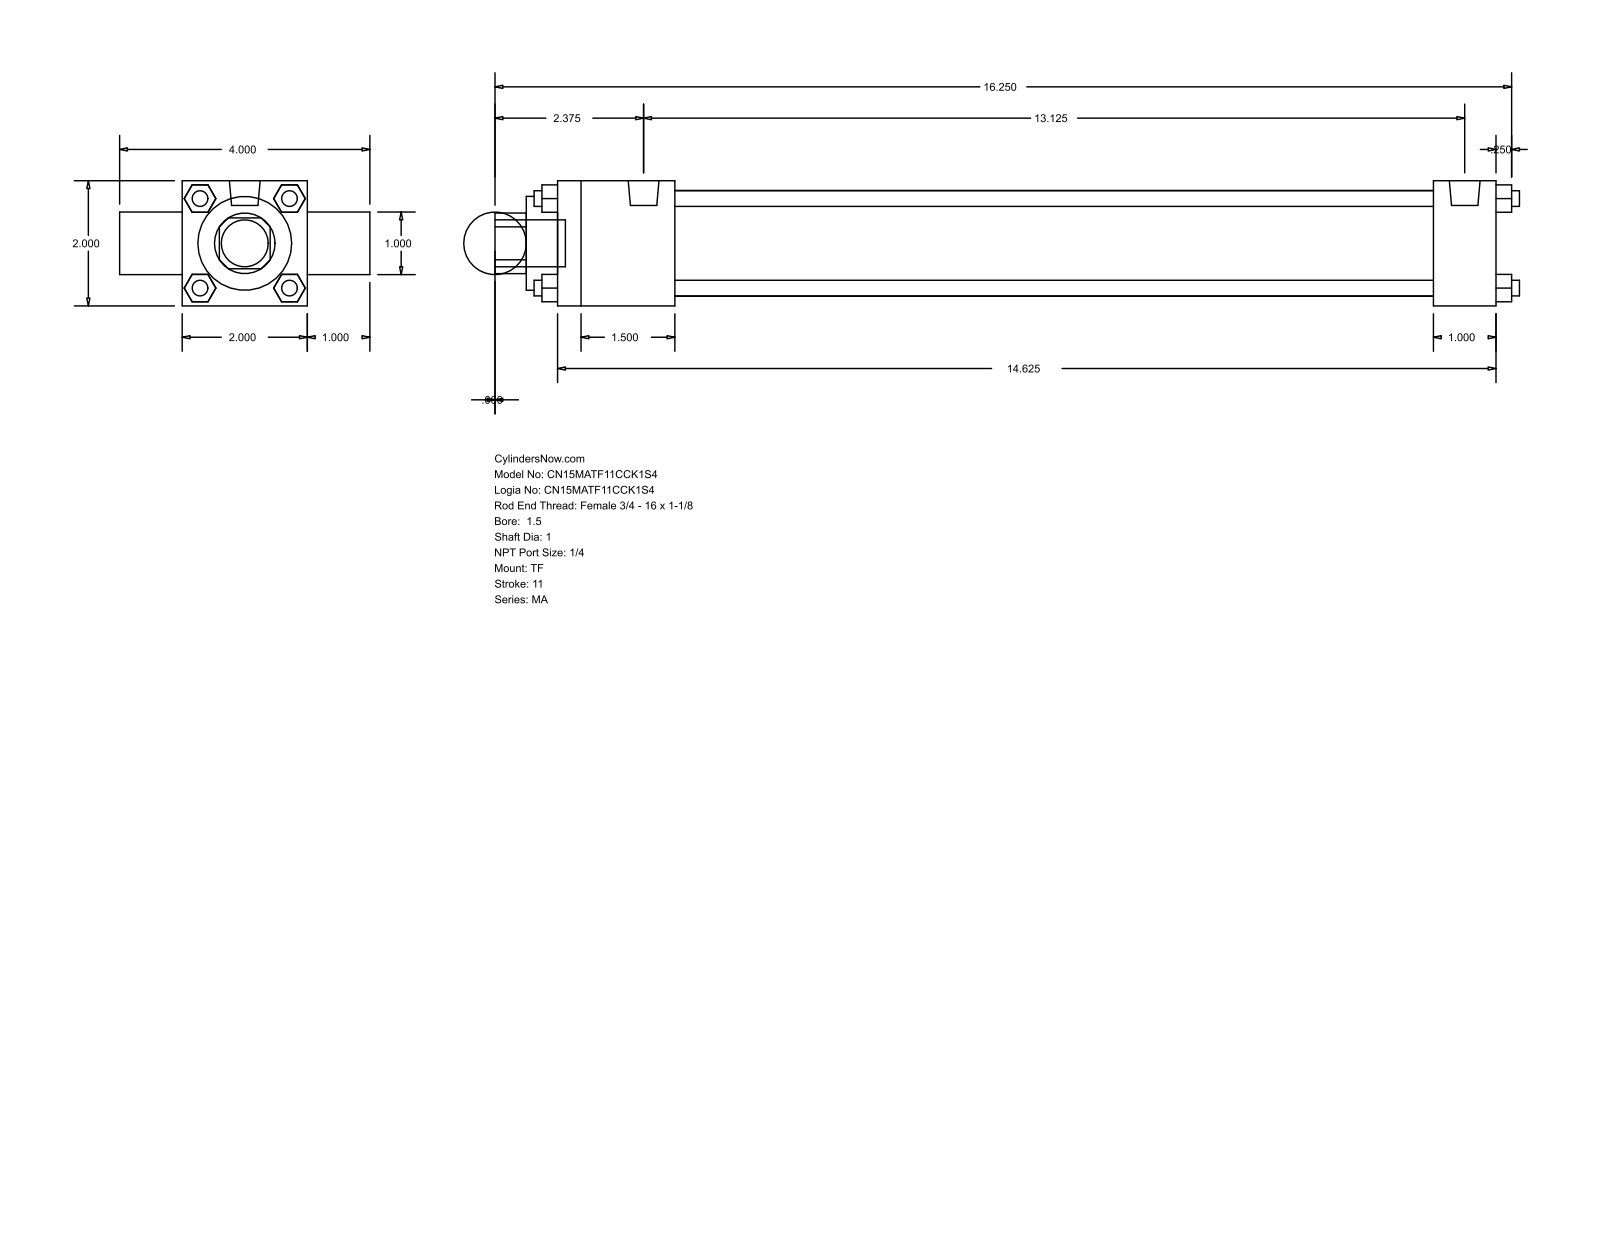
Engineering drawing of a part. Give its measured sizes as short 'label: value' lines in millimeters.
name: MA_TF__0150_1
written by: GSSL Pune (CONFIG_CONTROL_DESIGN)
unit: mm
bodies: 0 solids, 120 faces (92 planar, 28 cylindrical, 0 other)
size: 415.93 × 101.6 × 50.8
holes: 2× ⌀25.4, 1× ⌀38.1, 1× ⌀42.93
bosses: 4× ⌀6.35, 3× ⌀7.94, 2× ⌀12.49, 1× ⌀19.05
rounds: 1× R12.29
face distances: 50.8, 25.4, 381, 76.2, 6.35, 47.63, 355.6, 307.97, 333.37, 393.7
